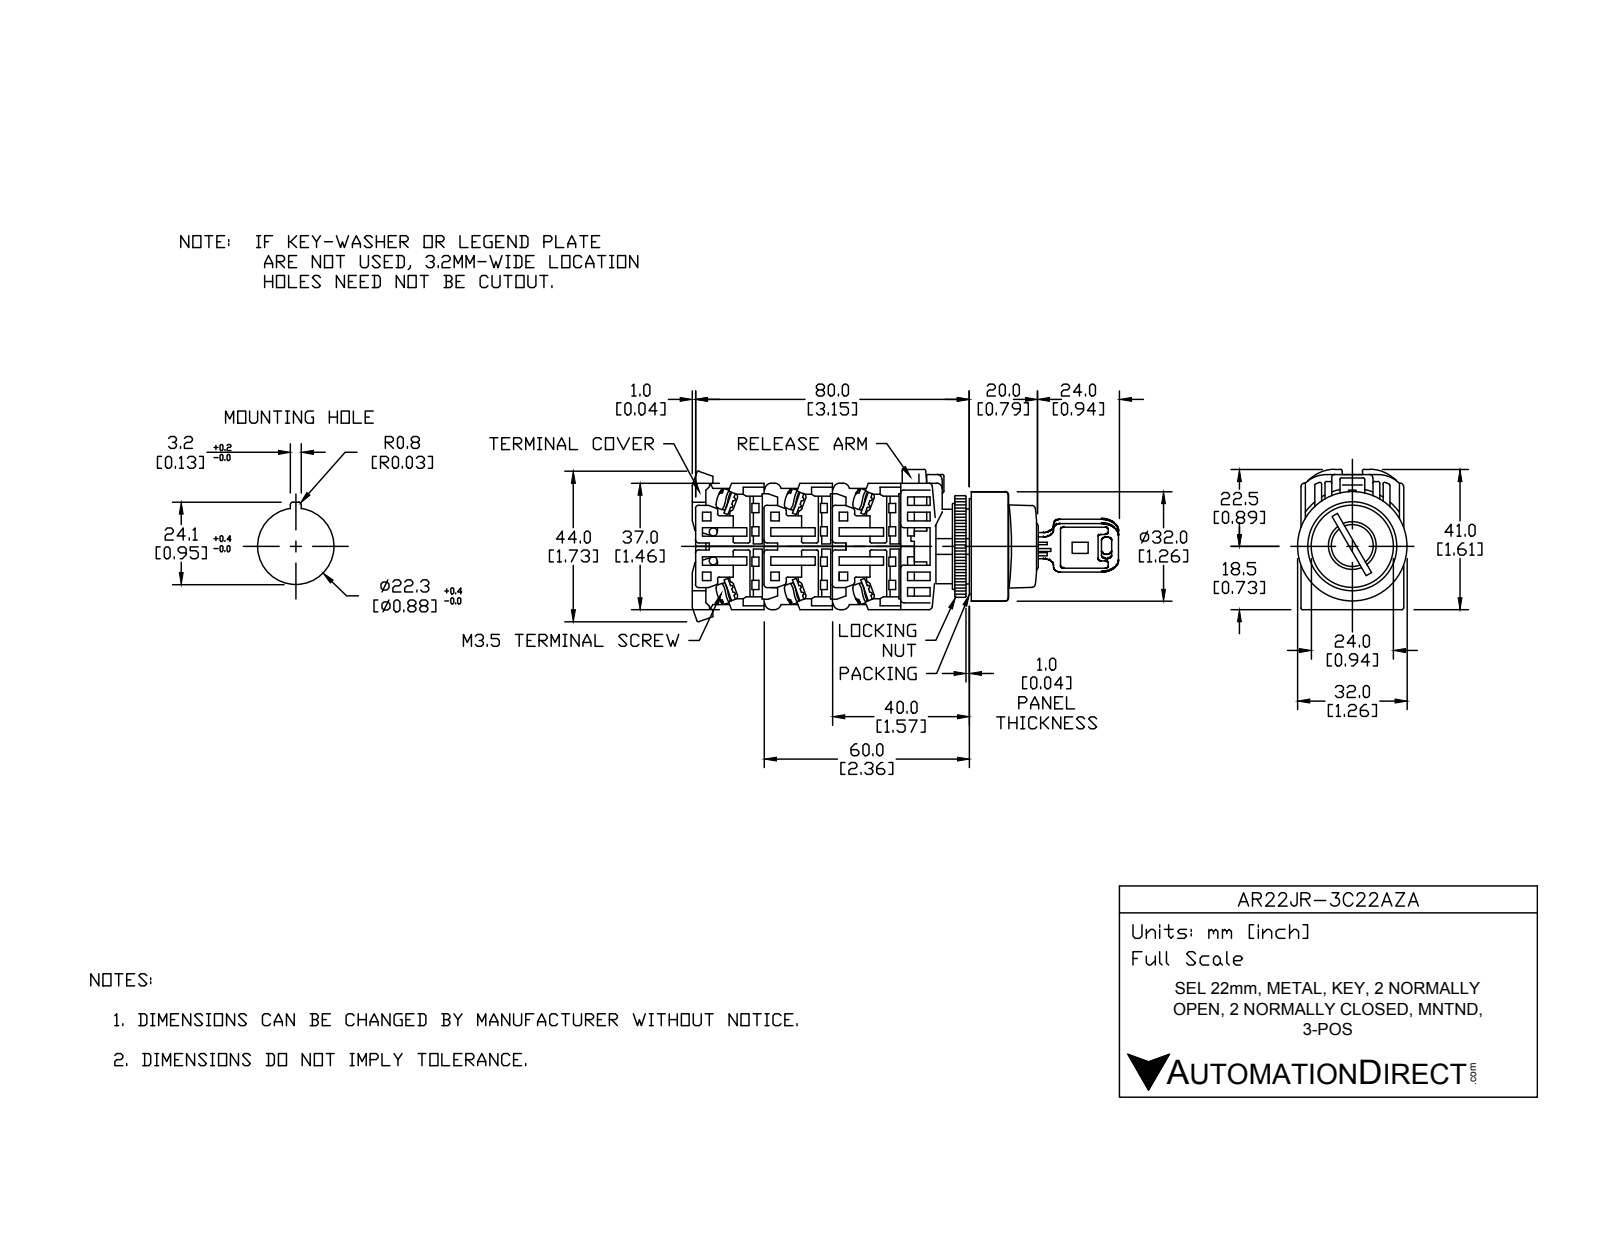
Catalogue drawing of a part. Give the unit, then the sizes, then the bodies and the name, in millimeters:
Units: millimetres
Overall size (bounding box): 61.5 × 43.81 × 32
Round holes (diameter × count): ⌀14 ×1, ⌀21.8 ×1, ⌀22 ×1, ⌀25 ×1, ⌀31 ×1
Round bosses / shafts (diameter × count): ⌀5 ×4, ⌀32 ×1, ⌀30.5 ×1, ⌀29.8 ×1, ⌀24 ×1, ⌀21.75 ×1, ⌀17 ×1, ⌀13.8 ×1
Partial cylindrical surfaces — rounded edges, fillets, slot ends (radius × count): R0.5 ×39, R1.75 ×8, R5 ×4, R4 ×2, R16.59 ×1, R17.59 ×1
Main face-to-face distances: 1, 20, 18, 28.5, 48.5, 29, 3, 9, 21, 10.5
Volume: 40 044 mm³ · Surface area: 25 929 mm²
Bodies: 19 solids, 448 faces (304 planar, 115 cylindrical, 29 other)
Part name (STEP PRODUCT): AR22JR-3C22AZA
STEP written by: SolidWorks 2017 (AUTOMOTIVE_DESIGN)
